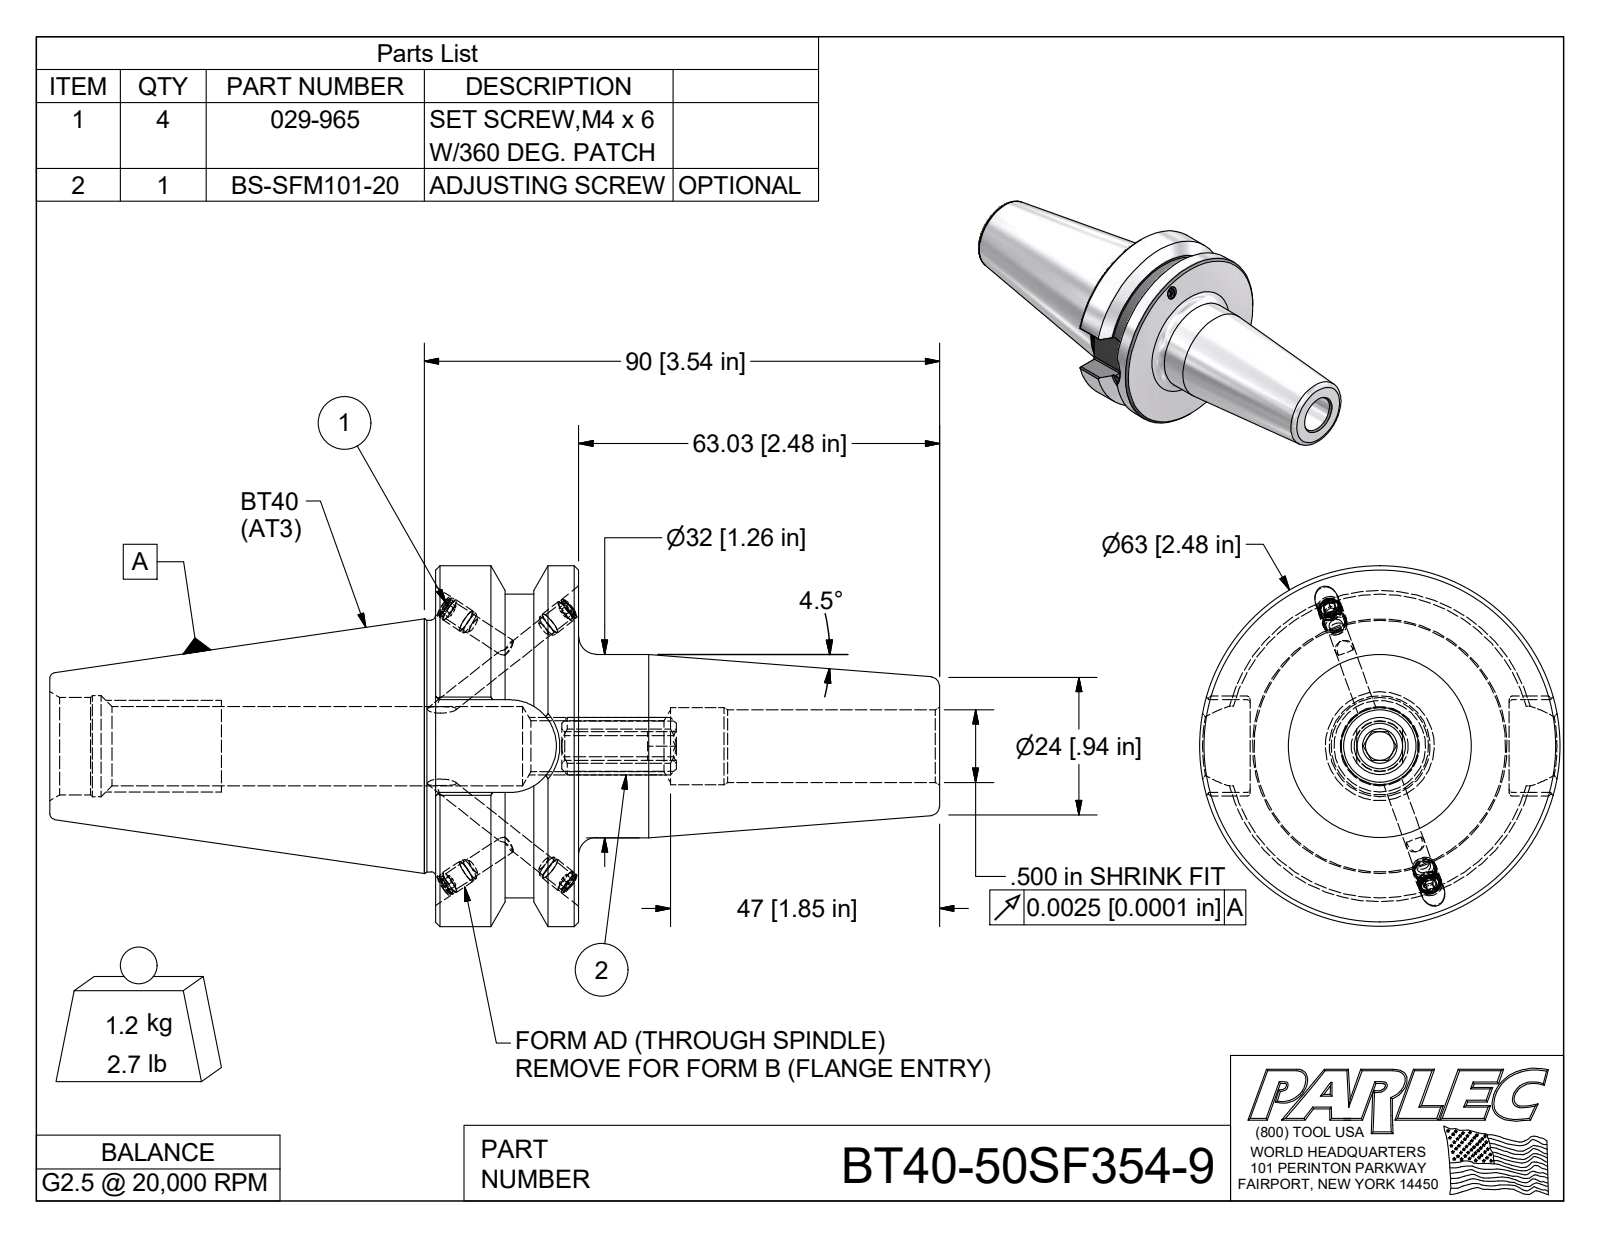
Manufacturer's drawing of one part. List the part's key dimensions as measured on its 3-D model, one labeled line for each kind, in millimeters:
Part name (STEP PRODUCT): BT40-50SF354-9; BT40BC-50SF354-9-1; 029-965; BS-SFM101-20
STEP written by: Autodesk Inventor 2009 (AUTOMOTIVE_DESIGN)
Units: millimetres
Bodies: 6 solids, 173 faces (79 planar, 43 cylindrical, 51 other)
Overall size (bounding box): 155.4 × 63 × 63
Volume: 155 000 mm³ · Surface area: 32 130 mm²
Round holes (diameter × count): ⌀3.3 ×4, ⌀4.1 ×4, ⌀12.7 ×1, ⌀13.4 ×1, ⌀17.6 ×1
Round bosses / shafts (diameter × count): ⌀4.2 ×4, ⌀4 ×4, ⌀63 ×1, ⌀53 ×1, ⌀44.5 ×1, ⌀43.9 ×1, ⌀32 ×1
Partial cylindrical surfaces — rounded edges, fillets, slot ends (radius × count): R0.5 ×8, R5 ×1, R8.1 ×1
Main face-to-face distances: 25, 45.2, 18.6, 26.6, 88, 63, 67.4, 92.4, 155.4, 16.2
